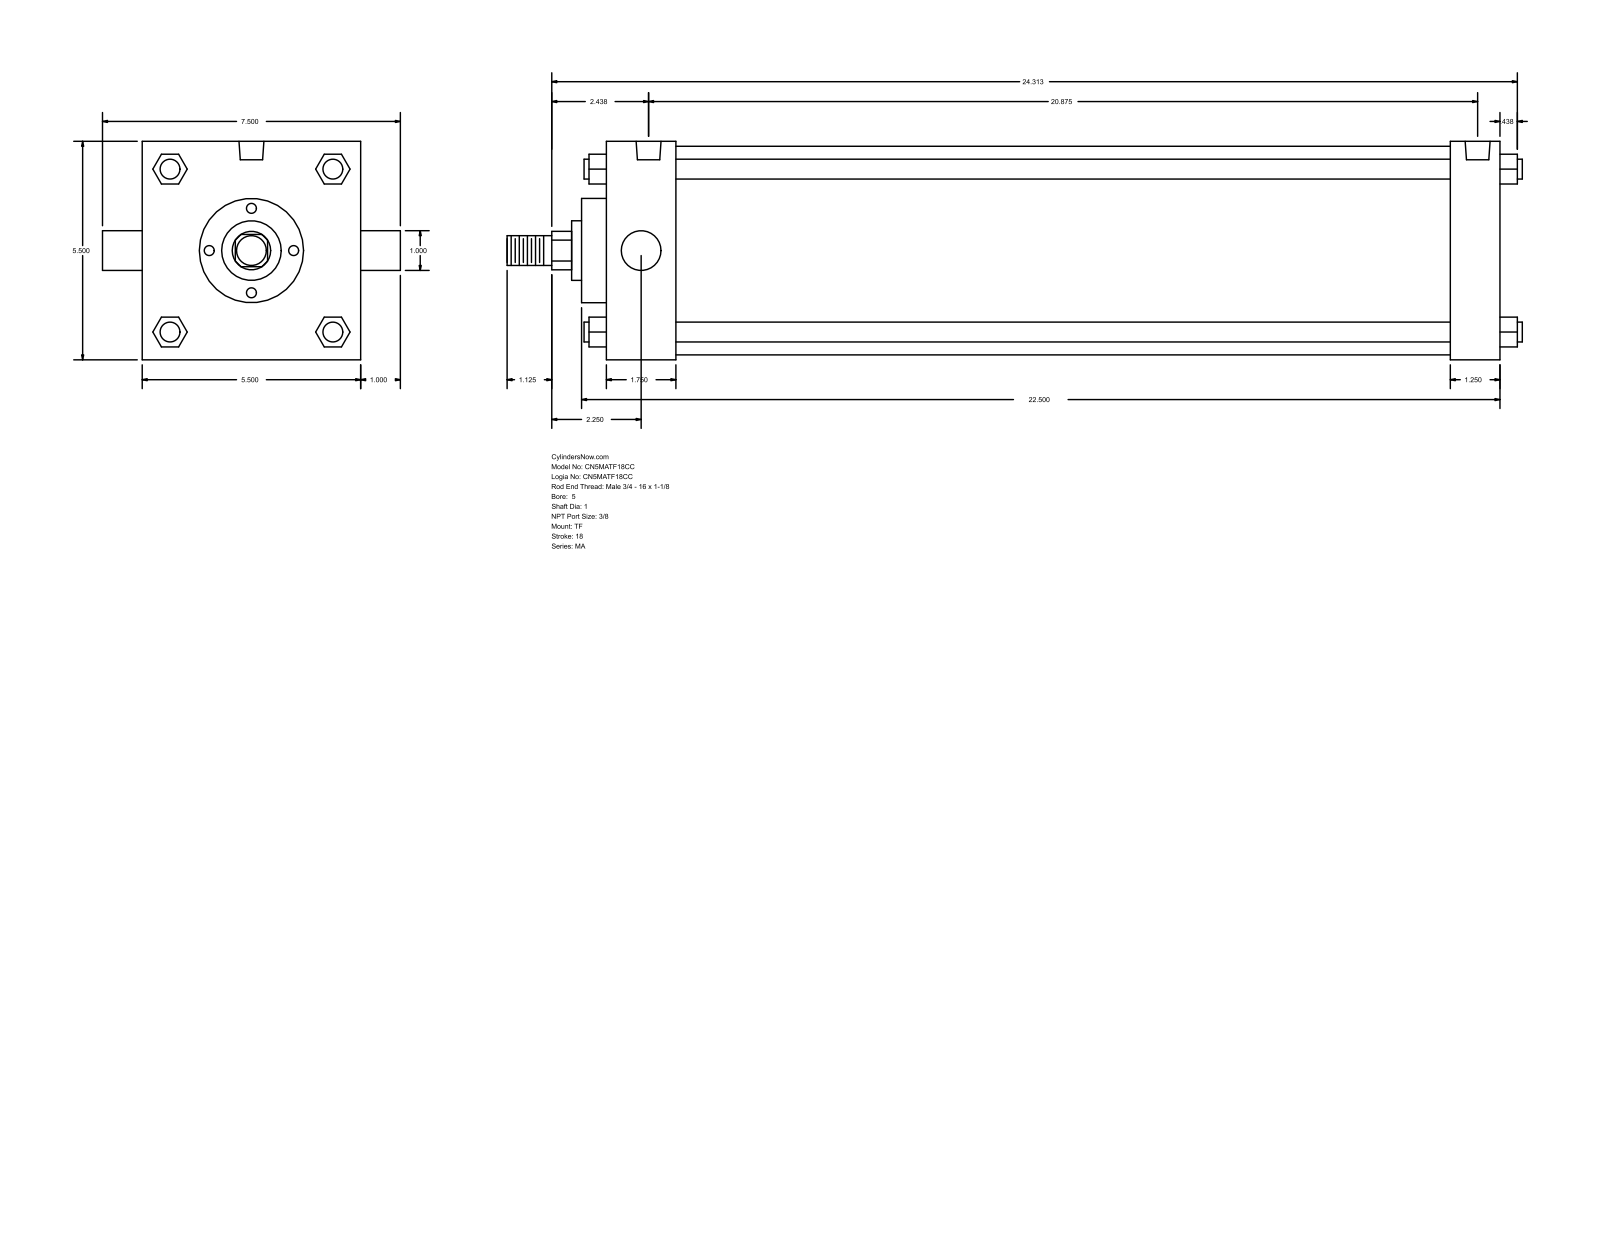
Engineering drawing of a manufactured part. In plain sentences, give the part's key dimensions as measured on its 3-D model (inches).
The part is named "MA_TF__0500_1". Its 3-D file was written by "GSSL Pune (CONFIG_CONTROL_DESIGN)". It is 0 solids with 122 faces: 93 planar, 29 cylindrical and 0 other. Overall it measures 25.563 by 7.5 by 5.5 inches. Round holes: 3 of diameter 0.437, 2 of diameter 0.627. Round bosses or shafts: 4 of diameter 0.5, 2 of diameter 1, 1 of diameter 5.25, 1 of diameter 2.625, 1 of diameter 1.5, 1 of diameter 0.75. Partial cylindrical surfaces (rounded edges, fillets, slot ends): 1 of radius 0.484. The main face-to-face distances are 5.5, 22.5, 21.25, 1.25, 1.75, 19.5, 20.75, 0.625, 2.375, 21.875. The hole center spacings are 0.187, 20.688, 20.5, 20.875.
